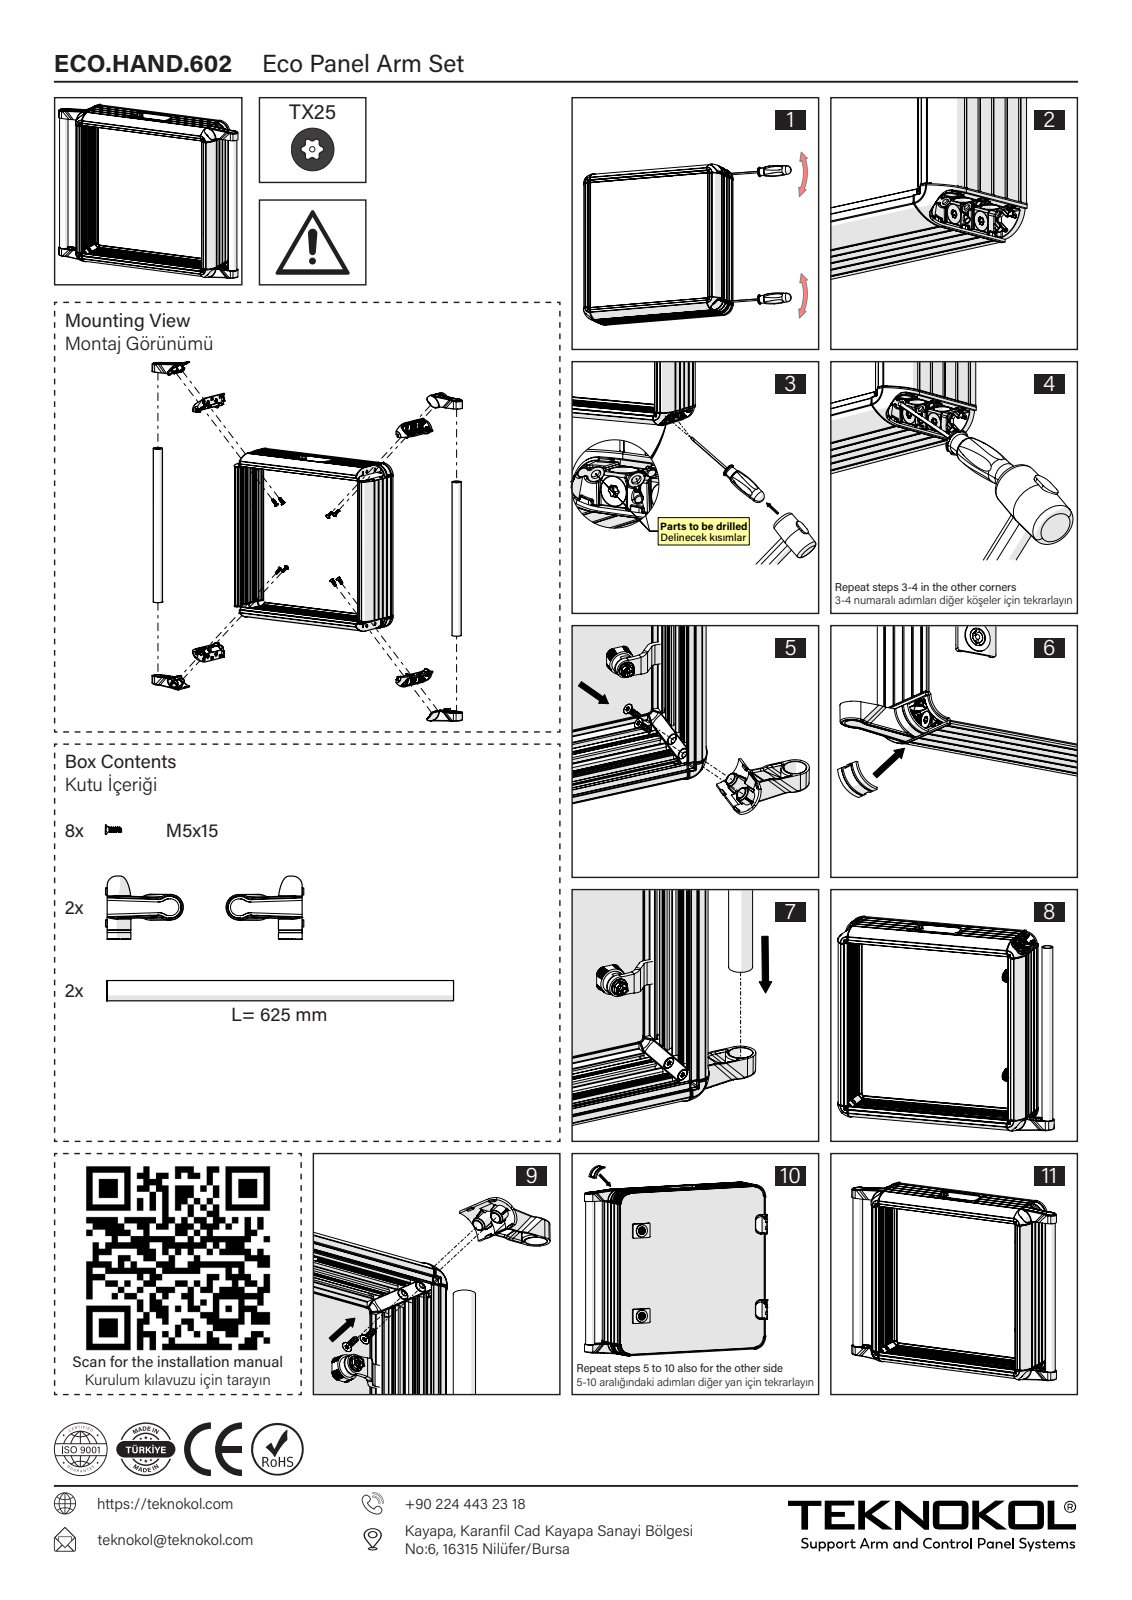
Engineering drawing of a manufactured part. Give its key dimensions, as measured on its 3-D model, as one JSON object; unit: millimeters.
{"part_name": "ECO.HAND.602", "step_written_by": "SolidWorks 2023 (AUTOMOTIVE_DESIGN)", "units": "millimeters", "bodies": {"solids": 22, "faces": 1738, "planar": 392, "cylindrical": 572, "other": 774}, "overall_size": [625, 103.7, 23.7], "volume_mm3": 129400, "surface_area_mm2": 199400, "round_holes": [[5, 8], [9, 8], [19, 4], [17, 2]], "round_bosses_or_shafts": [[9, 4], [2.8, 4], [19, 2]], "partial_cylinders_radius": [[0.3, 136], [1.5, 28], [0.4, 24], [1, 24], [3, 24], [1.2, 16], [1.7, 16], [1.4, 4]], "face_to_face_distances": [38.3, 2.5, 15.4, 35.8, 40.8, 2.2, 2.3, 2.3, 308.4, 313.7], "hole_center_spacings": [24, 27.9, 311.1, 311.1, 312, 312, 440, 23]}
